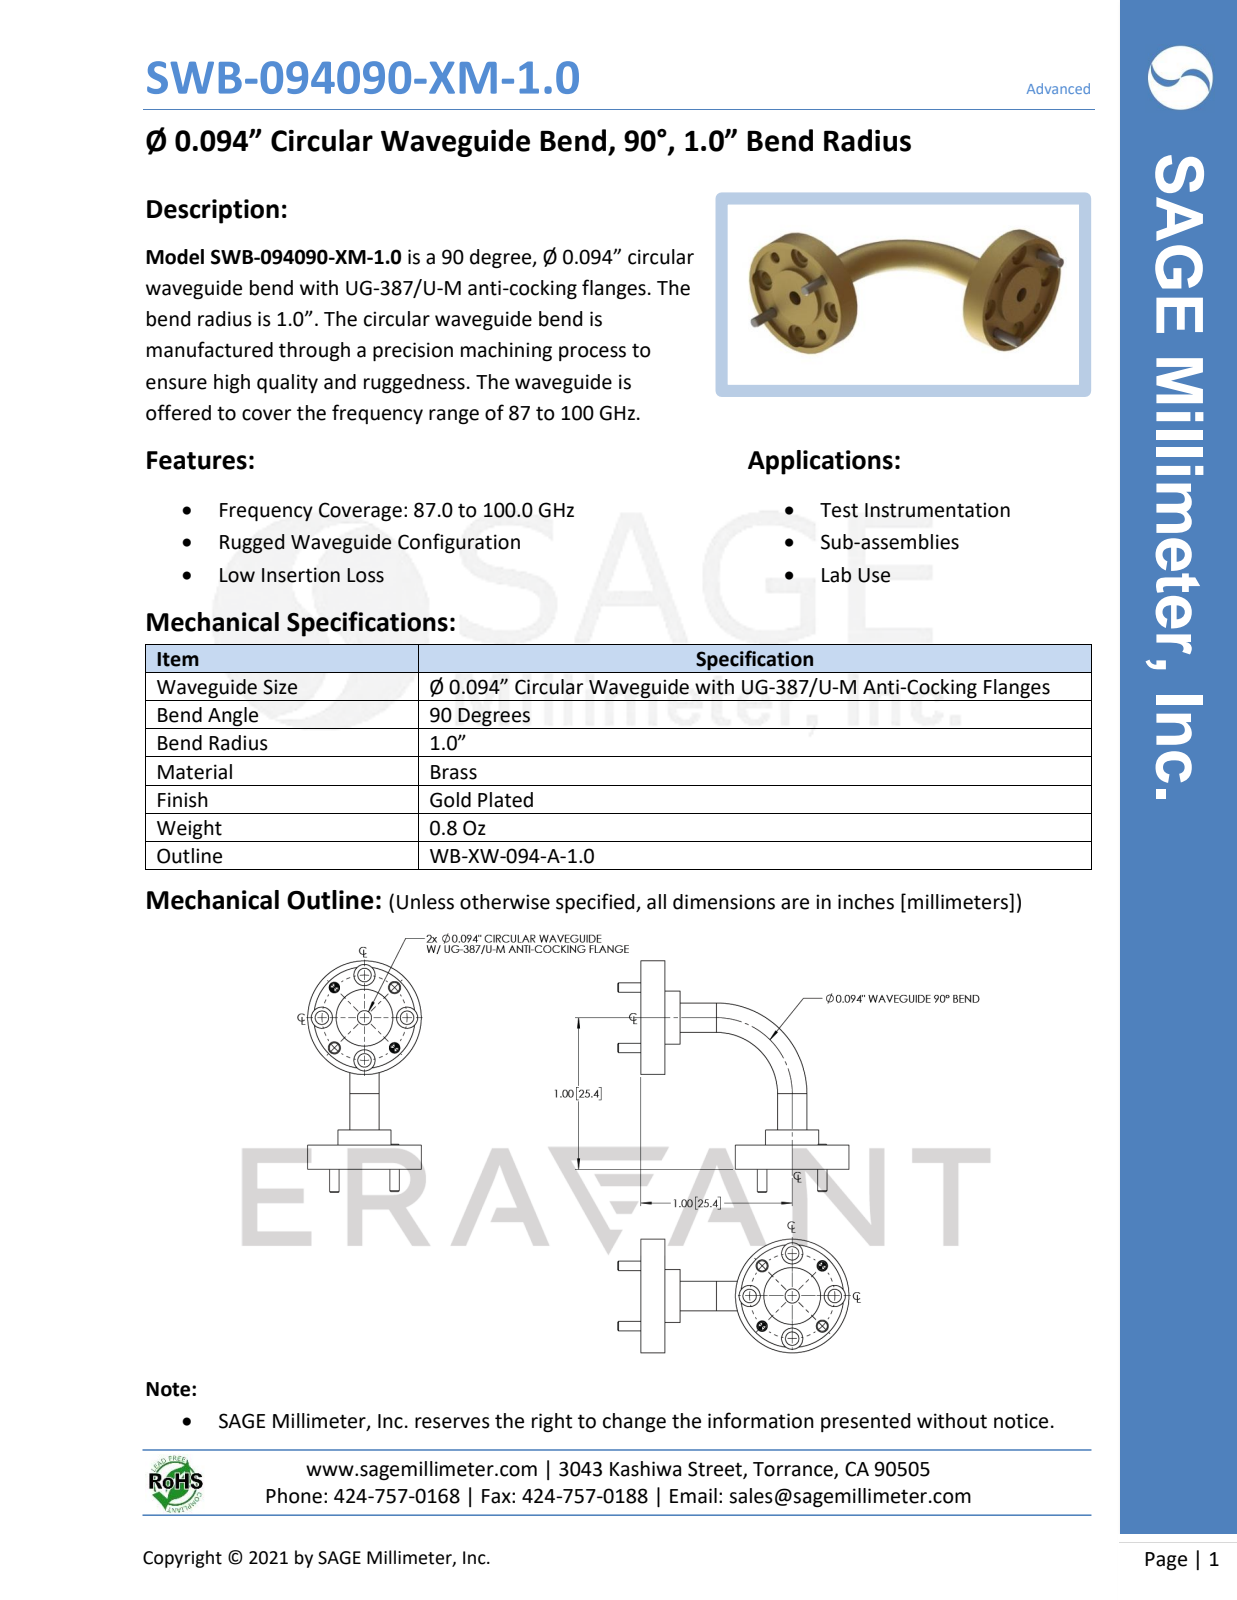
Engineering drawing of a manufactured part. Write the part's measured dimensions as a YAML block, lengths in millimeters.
part_name: "SWB-094090-XM-1.0"
step_written_by: "SolidWorks 2020 (CONFIG_CONTROL_DESIGN)"
units: millimeters
bodies: {solids: 5, faces: 146, planar: 28, cylindrical: 84, other: 34}
overall_size: [38.8, 38.8, 19.1]
volume: 2870
surface_area: 2778
round_holes:
  - {diameter: 2.3, count: 8}
  - {diameter: 3.6, count: 8}
  - {diameter: 1.5, count: 4}
  - {diameter: 1.7, count: 4}
  - {diameter: 2.4, count: 2}
  - {diameter: 17, count: 1}
  - {diameter: 17.3, count: 1}
round_bosses_or_shafts:
  - {diameter: 1.6, count: 4}
  - {diameter: 19.1, count: 2}
  - {diameter: 8.9, count: 2}
  - {diameter: 4.9, count: 2}
  - {diameter: 9.5, count: 1}
  - {diameter: 9.5, count: 1}
face_to_face_distances: [3.3, 0.8, 2.5, 4.1, 4.1, 0.8, 5.8, 5.1, 6.6, 6.6]
hole_center_spacings: [5.5, 10.1, 7.1, 13.2, 7.1, 14.3, 13.2, 10.1]
